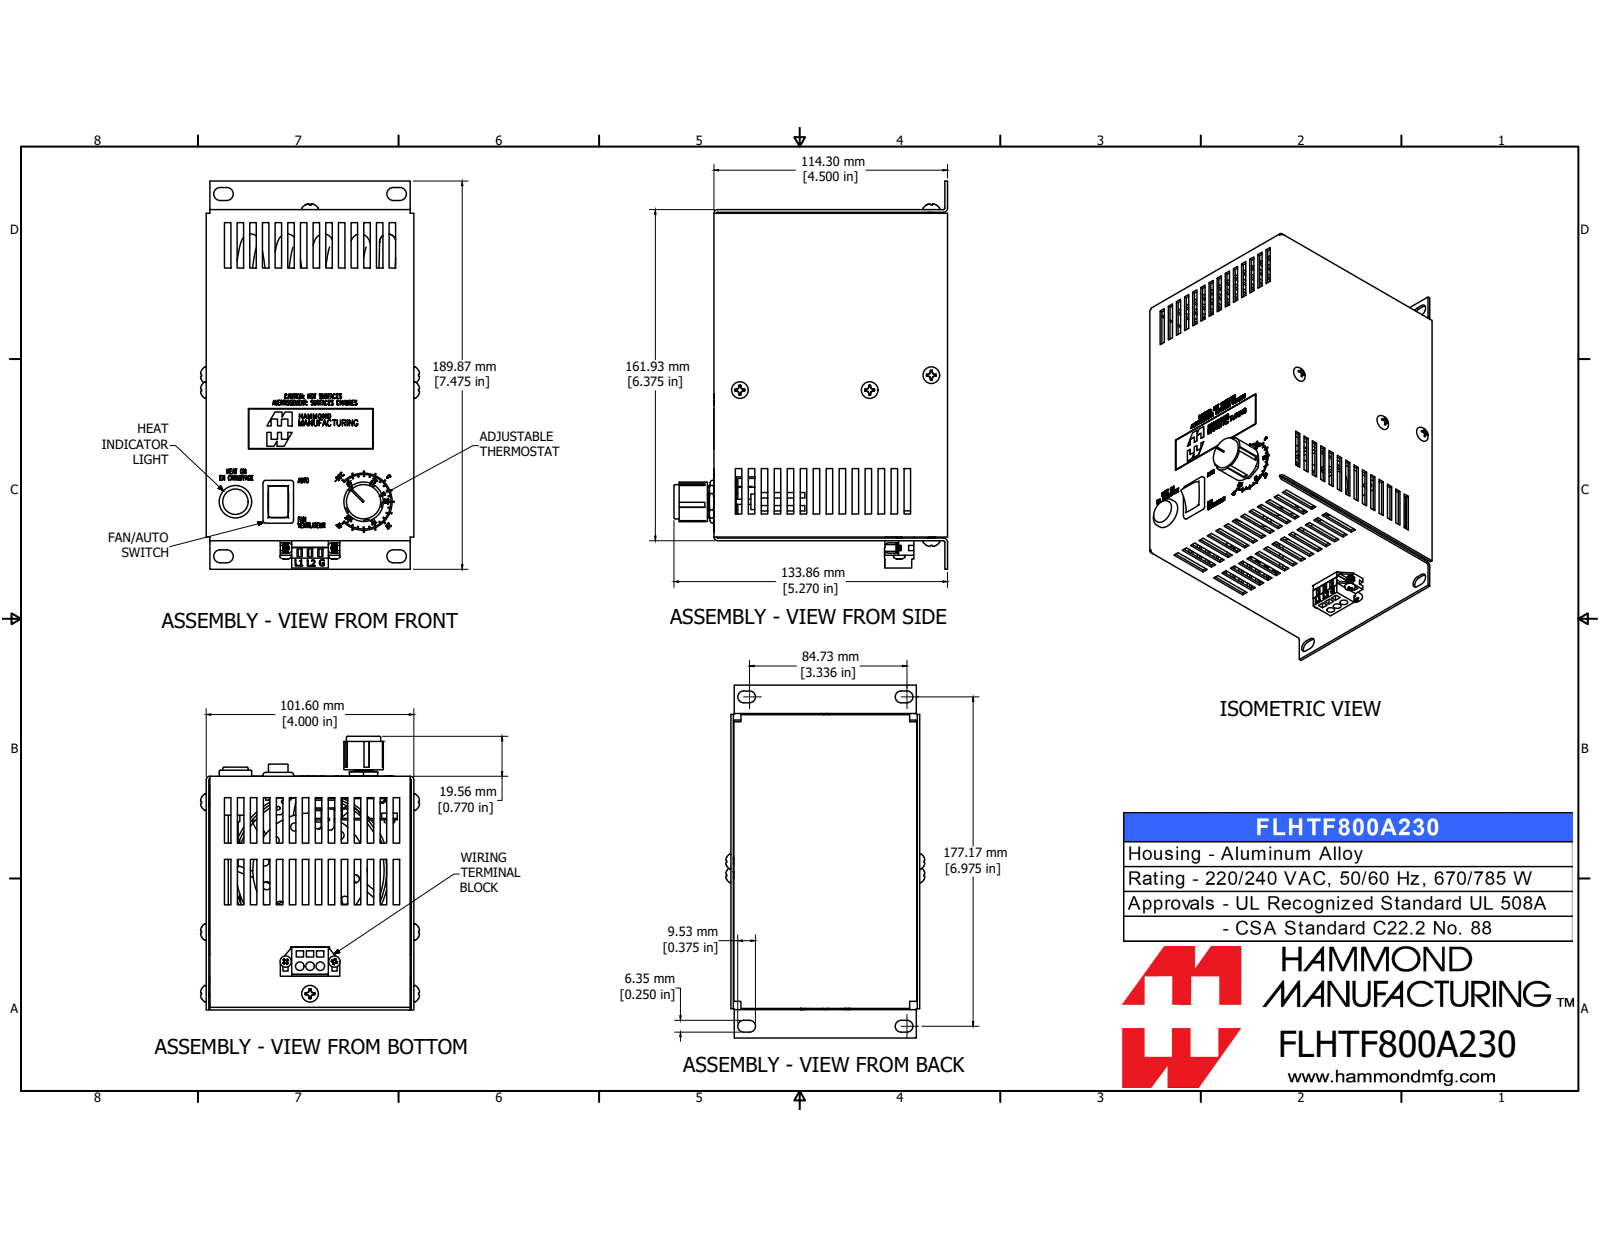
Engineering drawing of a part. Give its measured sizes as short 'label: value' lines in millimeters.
name: FLHTF800A230
written by: SolidWorks 2019 (AUTOMOTIVE_DESIGN)
unit: mm
bodies: 17 solids, 4241 faces (3722 planar, 274 cylindrical, 245 other)
size: 189.9 × 133.9 × 107.1
volume: 180 700 mm³; area: 222 600 mm²
holes: 4× ⌀3.5, 4× ⌀4.6, 4× ⌀5.2, 3× ⌀4.2, 2× ⌀2.2, 2× ⌀3, 2× ⌀3.3, 2× ⌀4.8, 1× ⌀1.7, 1× ⌀1.8, 1× ⌀6.4, 1× ⌀9.7
bosses: 4× ⌀4.2, 4× ⌀2.6, 2× ⌀4.3, 2× ⌀2.7, 1× ⌀19.3, 1× ⌀16.8, 1× ⌀16.5, 1× ⌀15.9
rounds: 38× R3.2, 17× R1.3, 12× R16, 9× R3.8, 8× R0.6, 4× R0.5, 4× R1.8, 2× R0.4
face distances: 1.3, 100.3, 2.5, 1.3, 160.6, 101.6, 99, 112.8, 114.1, 110.3
hole spacings: 70, 5, 7.3, 12.1, 14.3, 14.4, 17.1, 19.7
